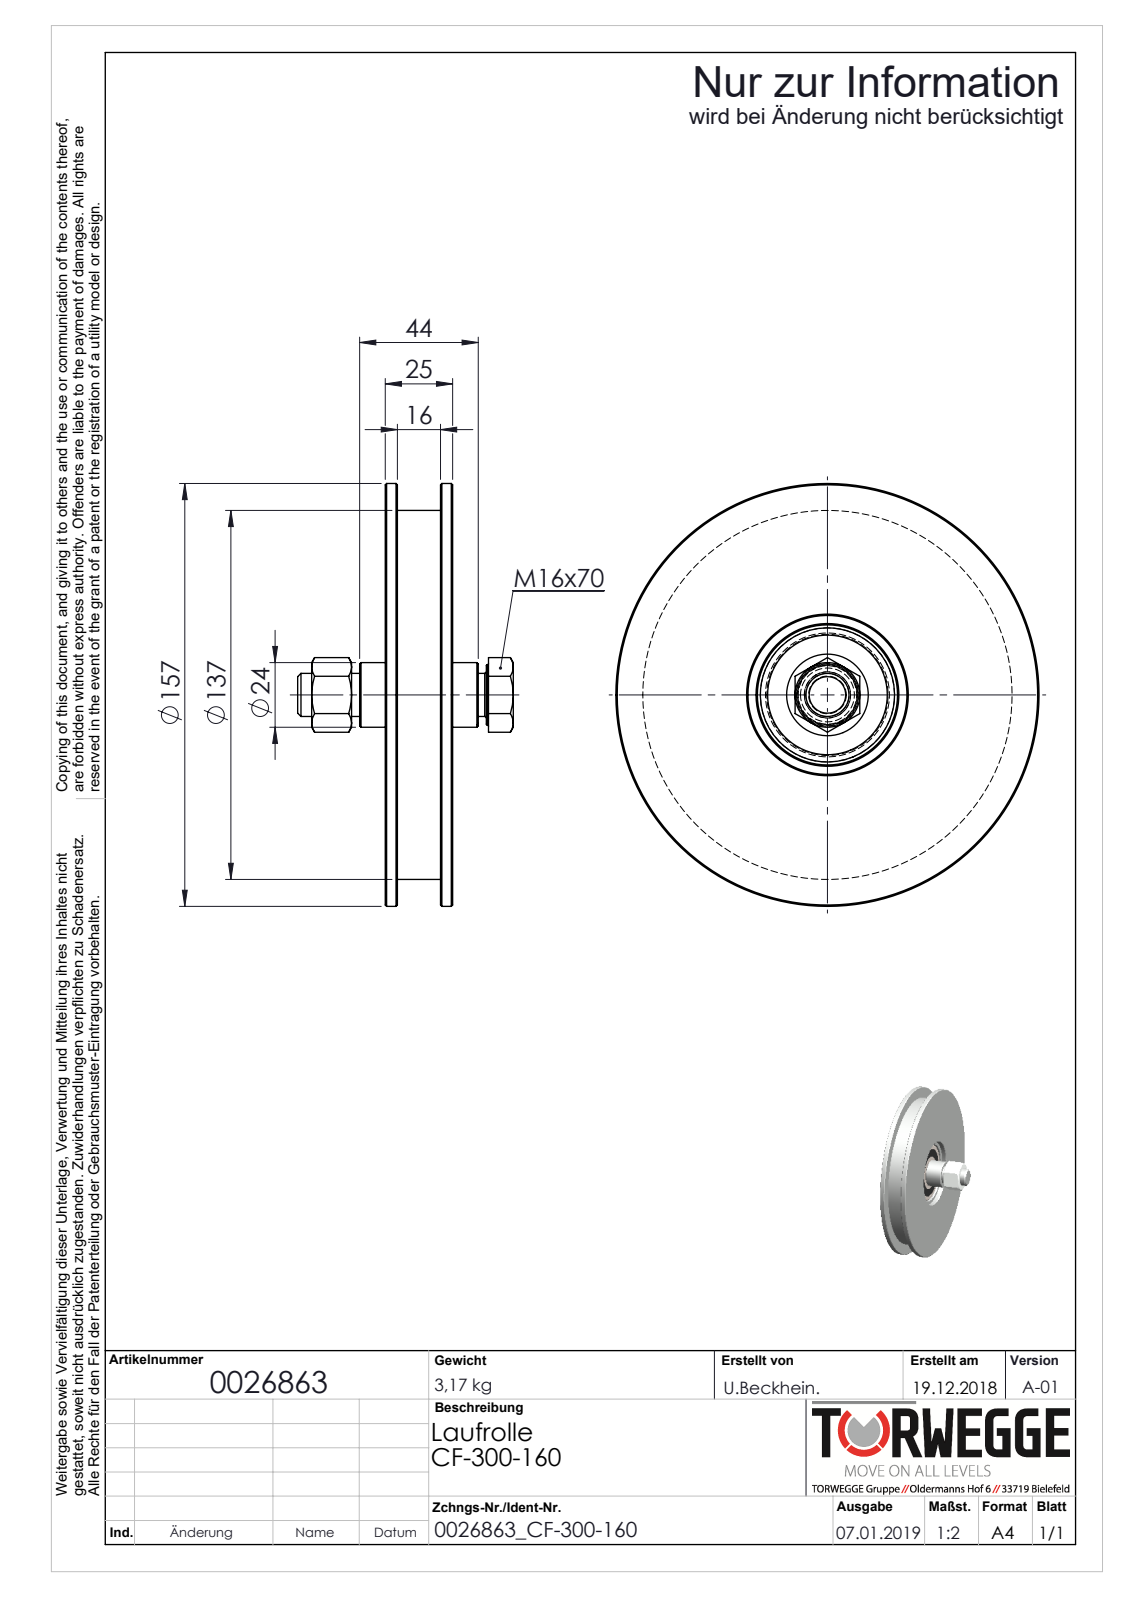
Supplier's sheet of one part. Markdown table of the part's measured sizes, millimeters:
| quantity | value |
| --- | --- |
| part name | 0026863_CF-300-160_(A-01) |
| STEP written by | SolidWorks 2018 (AUTOMOTIVE_DESIGN) |
| units | millimeters |
| bodies | 0 solids, 144 faces (36 planar, 42 cylindrical, 66 other) |
| overall size | 157 × 157 × 80 |
| round holes (diameter × count) | 14 × 1, 16 × 1, 16.1 × 1, 44.4 × 1, 45 × 1, 52 × 1, 59 × 1 |
| round bosses / shafts (diameter × count) | 157 × 1, 137 × 1, 30.3 × 1, 24 × 1, 20 × 1 |
| main face-to-face distances | 25, 4.5, 20.5, 16, 0.5, 20, 5, 15.5, 5.1, 19.9 |
